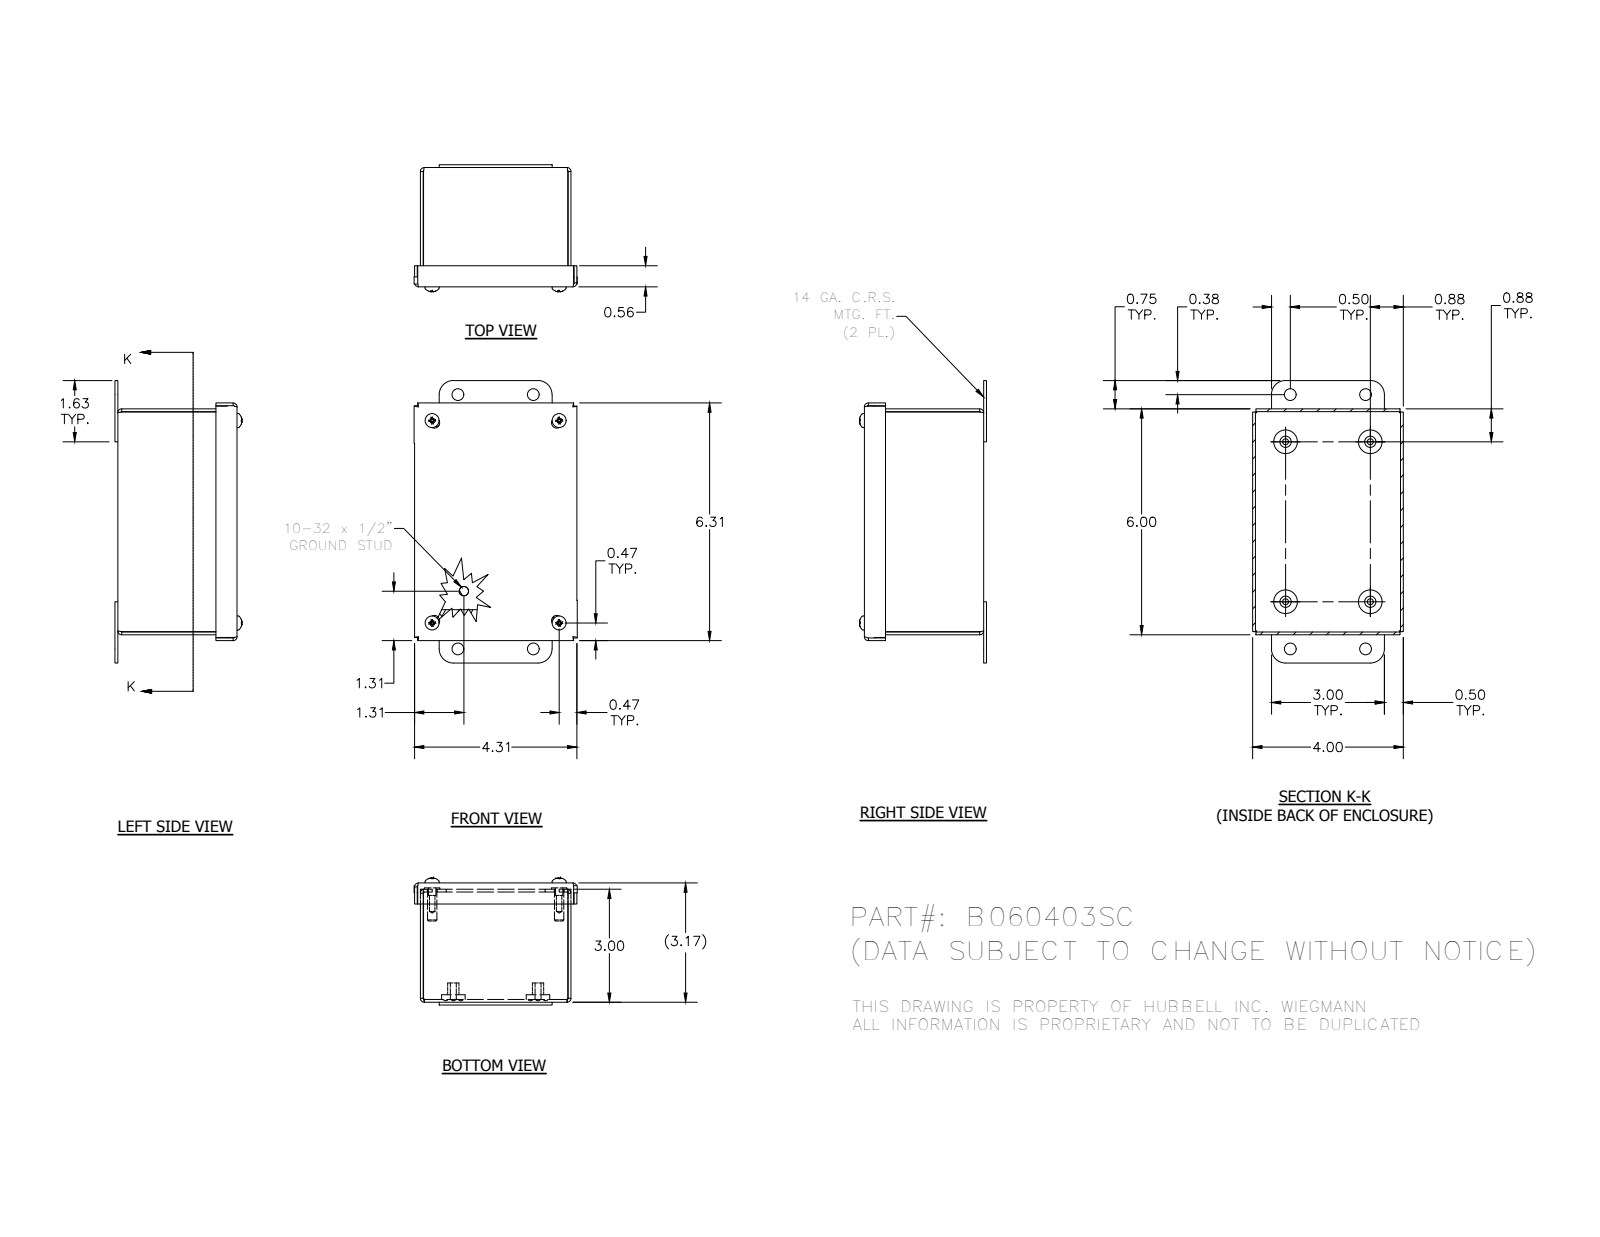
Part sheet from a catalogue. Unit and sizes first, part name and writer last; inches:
Units: inches
Overall size (bounding box): 7.5 × 4.336 × 3.346
Round holes (diameter × count): ⌀0.145 ×4, ⌀0.156 ×4, ⌀0.196 ×4, ⌀0.278 ×4, ⌀0.281 ×4, ⌀0.31 ×4, ⌀0.313 ×4
Round bosses / shafts (diameter × count): ⌀0.19 ×5, ⌀0.625 ×4, ⌀0.453 ×4, ⌀0.406 ×4, ⌀0.373 ×4, ⌀0.3 ×4, ⌀0.248 ×4, ⌀0.25 ×1
Partial cylindrical surfaces — rounded edges, fillets, slot ends (radius × count): R0.031 ×12, R0.105 ×12, R0.089 ×4, R0.375 ×4
Main face-to-face distances: 0.074, 3.094, 3.926, 3.168, 3.02, 5.926, 3.852, 4, 0.156, 0.157
Hole centre spacings: 3.314, 5.314, 5.395, 0.087, 1.256, 2.774, 2.868, 3.375
Volume: 12.1 in³ · Surface area: 311.3 in²
Bodies: 23 solids, 532 faces (311 planar, 102 cylindrical, 119 other)
Part name (STEP PRODUCT): B060403SC; 3481; 34984; B060403SCBKP (+6 more)
STEP written by: Autodesk Inventor 2012 (AUTOMOTIVE_DESIGN)
